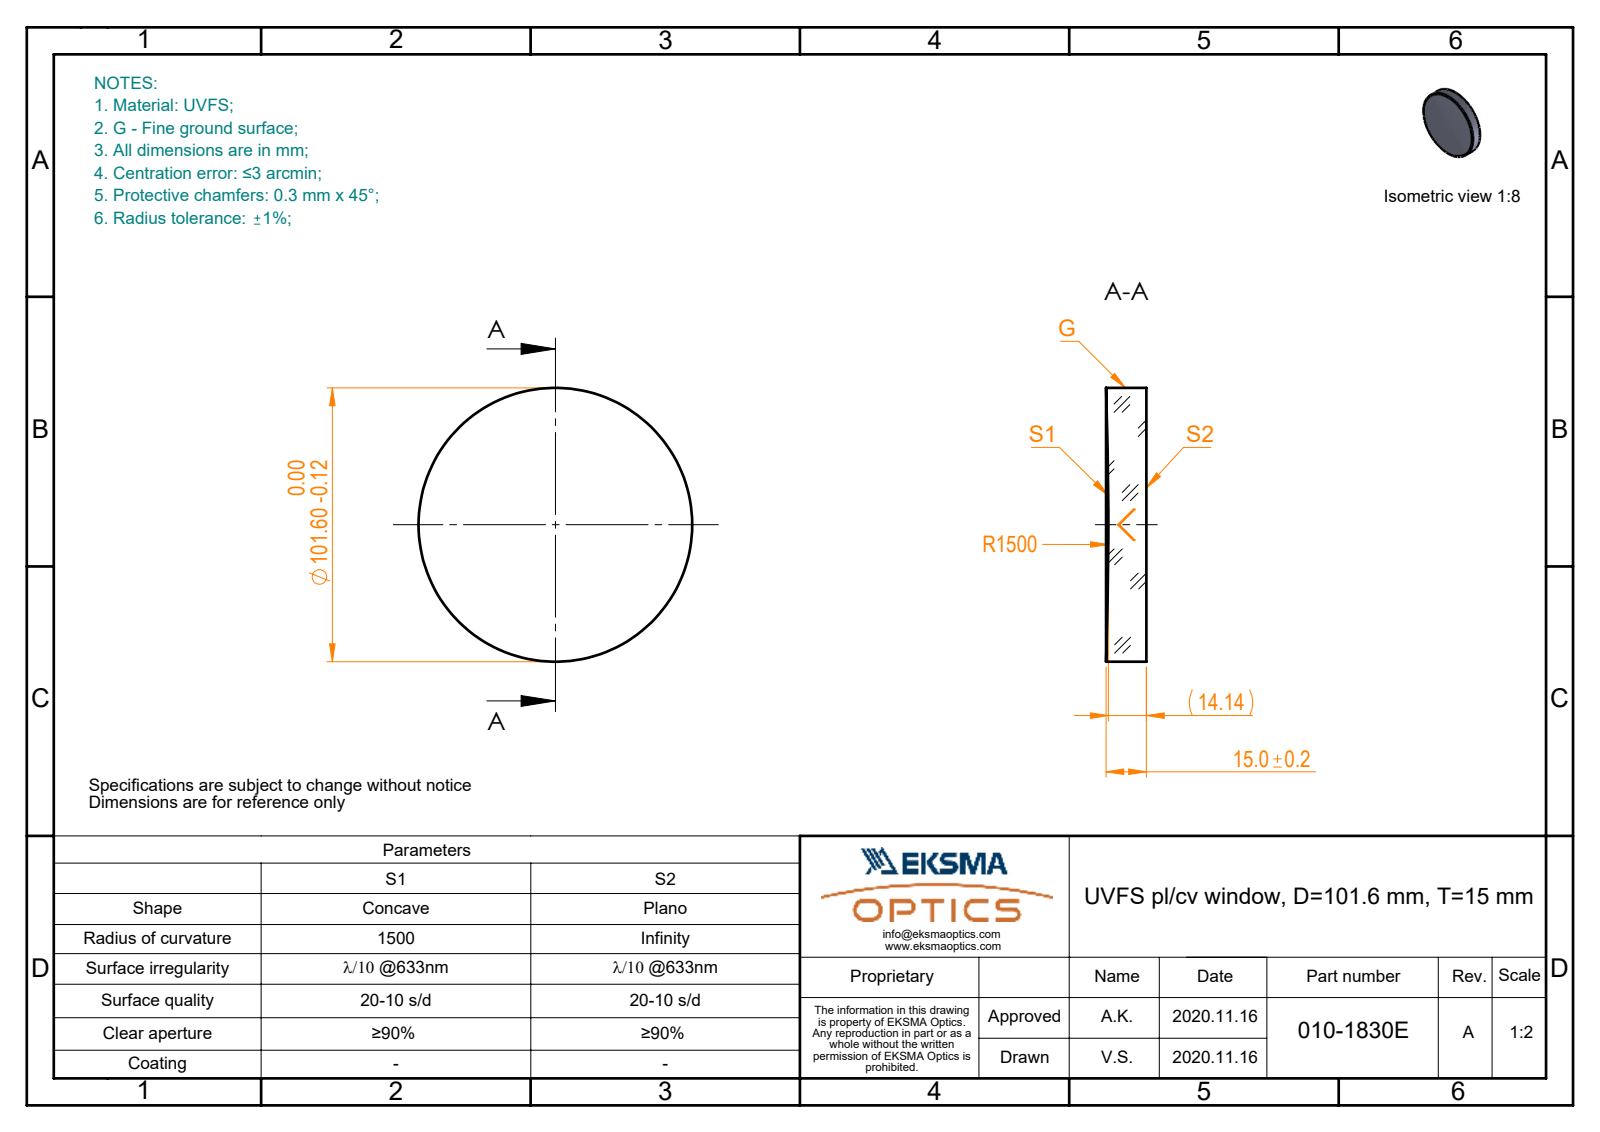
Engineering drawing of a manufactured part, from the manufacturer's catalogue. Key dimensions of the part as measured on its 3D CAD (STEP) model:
Part name (STEP PRODUCT): 010-1830E_UVFS_PCV_window
STEP written by: SolidWorks 2019 (CONFIG_CONTROL_DESIGN)
Units: millimetres
Bodies: 1 solid, 5 faces (1 planar, 2 cylindrical, 2 other)
Overall size (bounding box): 101.6 × 101.6 × 15
Volume: 118 121 mm³ · Surface area: 21 005 mm²
Round bosses / shafts (diameter × count): ⌀101.6 ×1
